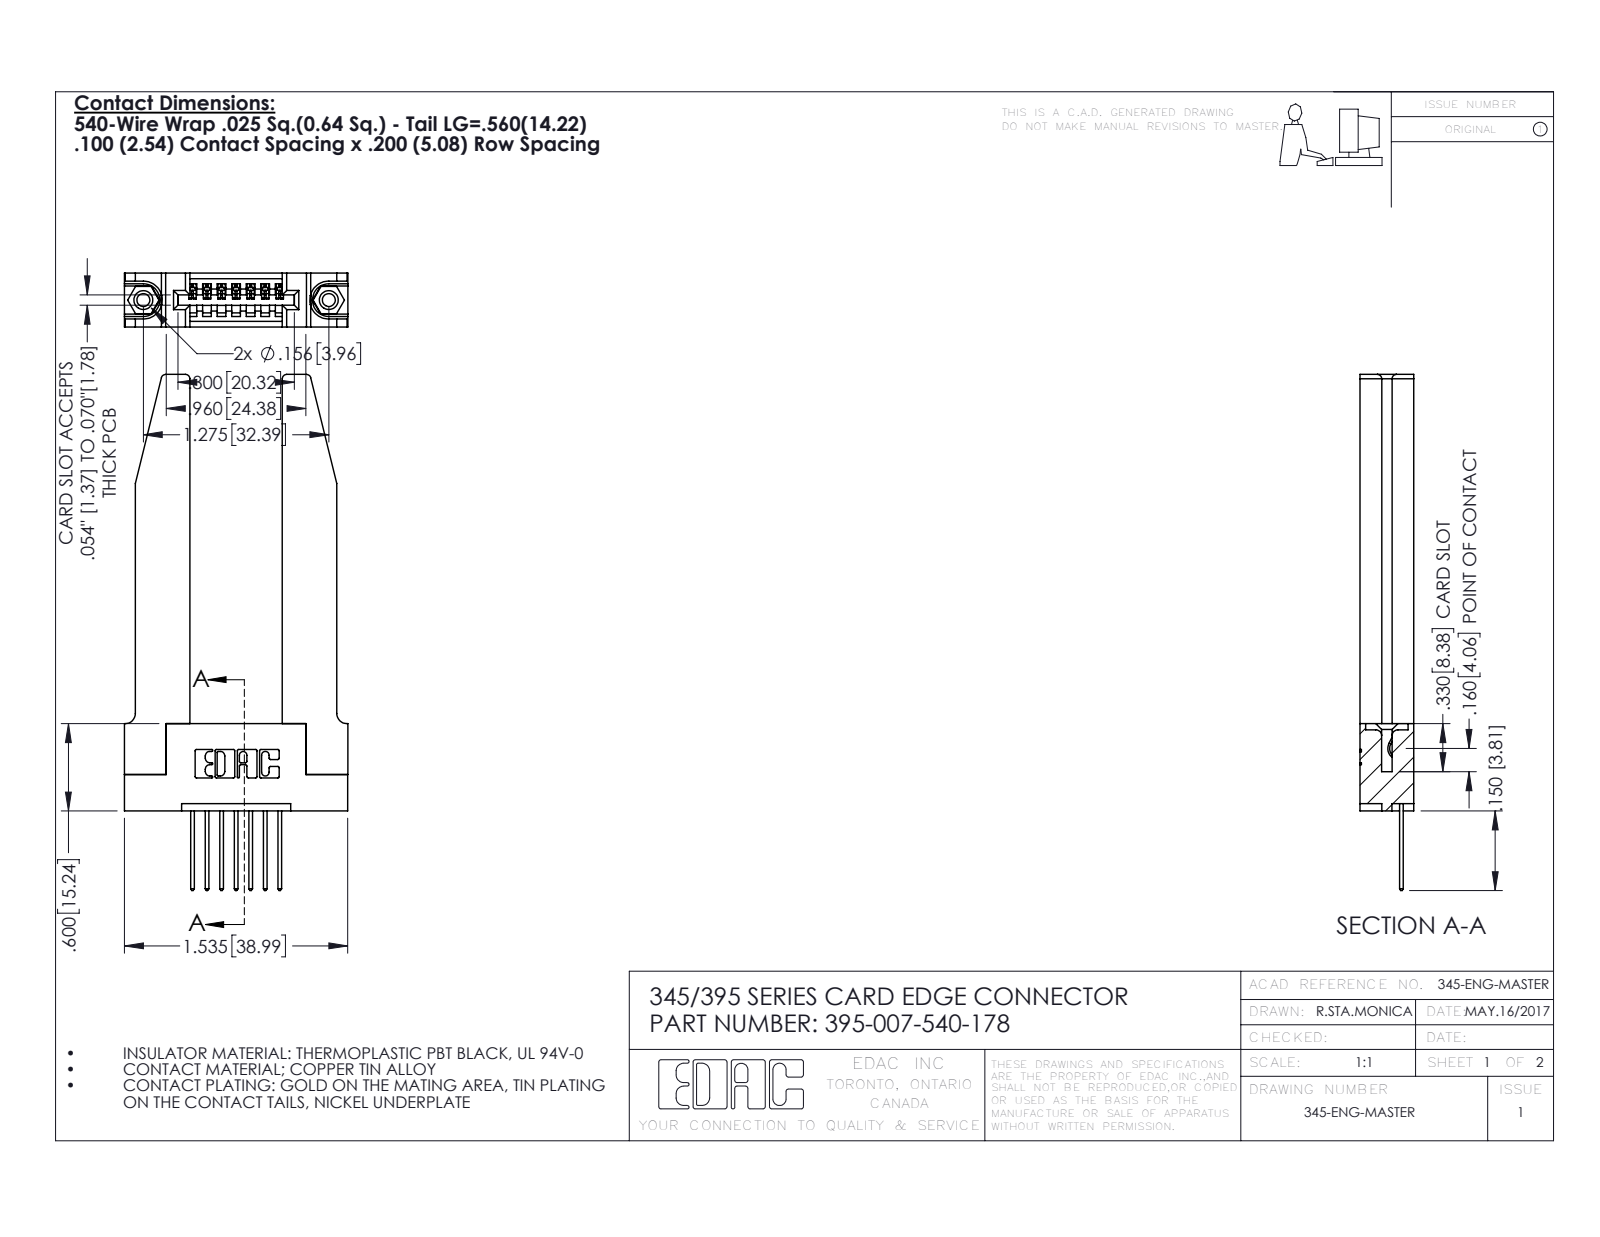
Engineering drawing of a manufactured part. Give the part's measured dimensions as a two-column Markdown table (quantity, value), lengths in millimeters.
| quantity | value |
| --- | --- |
| part name | 345 Part_Flush Mounting Lugs - 0.156 Dia-TH; 345-220-078_345-220-078; 345-250-001_345-250-001-102; 395-007-540-178 (+1 more) |
| STEP written by | SolidWorks 2016 (CONFIG_CONTROL_DESIGN) |
| units | millimeters |
| bodies | 12 solids, 766 faces (502 planar, 212 cylindrical, 52 other) |
| overall size | 90.1 × 39 × 9.4 |
| volume | 11 200 mm³ |
| surface area | 10 990 mm² |
| round holes (diameter × count) | 2.3 × 2, 3.2 × 2, 4 × 2, 1.6 × 1 |
| round bosses / shafts (diameter × count) | 3.9 × 2 |
| partial cylindrical surfaces (radius × count) | 0.3 × 22, 0.2 × 14, 0.3 × 14, 0.8 × 8, 0.2 × 6, 0.8 × 6, 0.7 × 3, 0.8 × 2 |
| main face-to-face distances | 9.4, 3.8, 1.8, 5.6, 7.6, 3.8, 16.1, 2, 5.1, 2.4 |
| hole center spacings | 6.9, 26.5, 32.4 |
